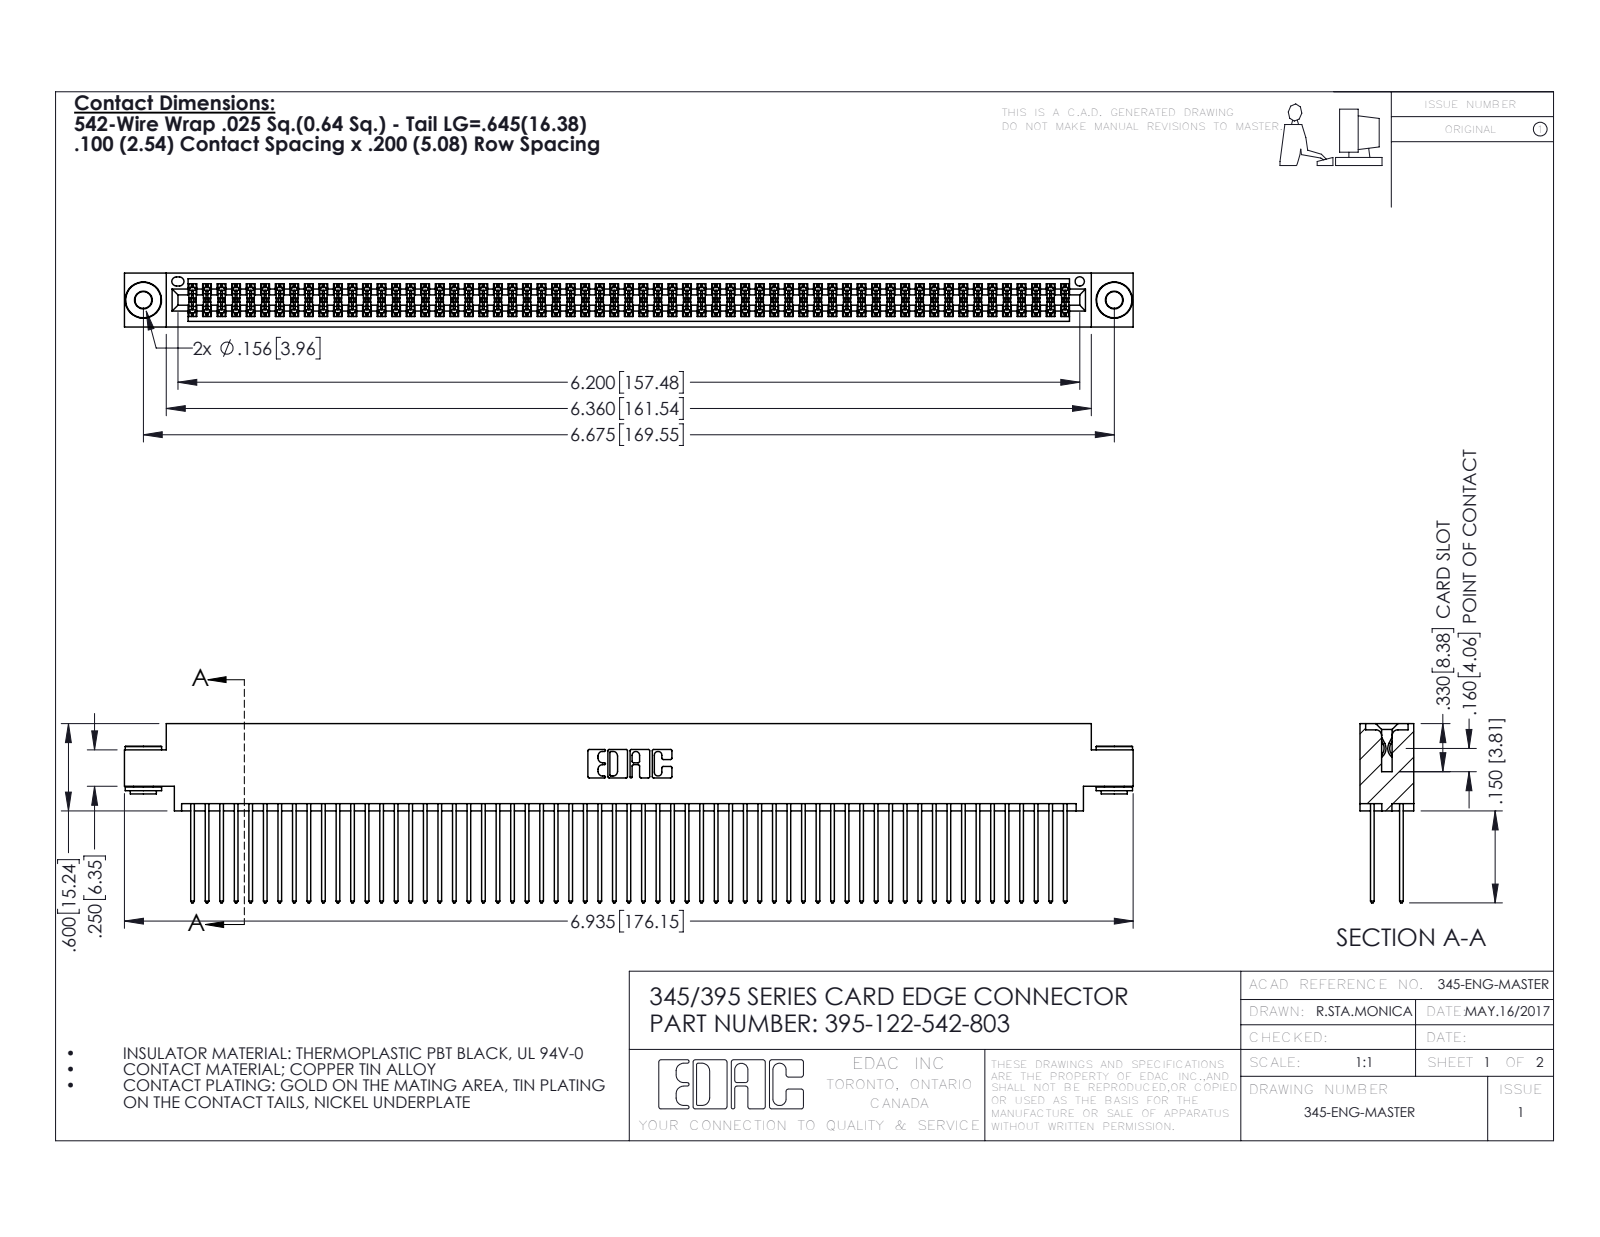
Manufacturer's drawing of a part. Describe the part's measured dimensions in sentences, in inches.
The part is named "395-122-542-803; 345-292-001_345-293-142; 345 Part_0.170 Offset - 0.156 Dia-TH; 345-250-002_345-250-002-102". Its 3-D file was written by "SolidWorks 2016 (CONFIG_CONTROL_DESIGN)". It is 125 solids with 6268 faces: 4120 planar, 2140 cylindrical and 8 other. Overall it measures 6.935 by 1.232 by 0.37 inches. Its volume is 1.084 cubic inches and its surface area 45.93 square inches. Round holes: 2 of diameter 0.116, 2 of diameter 0.156, 1 of diameter 0.064. Round bosses or shafts: 2 of diameter 0.25, 2 of diameter 0.18, 2 of diameter 0.136. Partial cylindrical surfaces (rounded edges, fillets, slot ends): 183 of radius 0.006, 122 of radius 0.01, 22 of radius 0.01, 6 of radius 0.007, 6 of radius 0.031, 3 of radius 0.026, 2 of radius 0.014, 2 of radius 0.019. The main face-to-face distances are 0.072, 0.298, 0.2, 0.098, 0.272, 0.025, 0.37, 0.225, 0.175, 0.149. The hole center spacings are 0.27, 6.439, 6.675.
